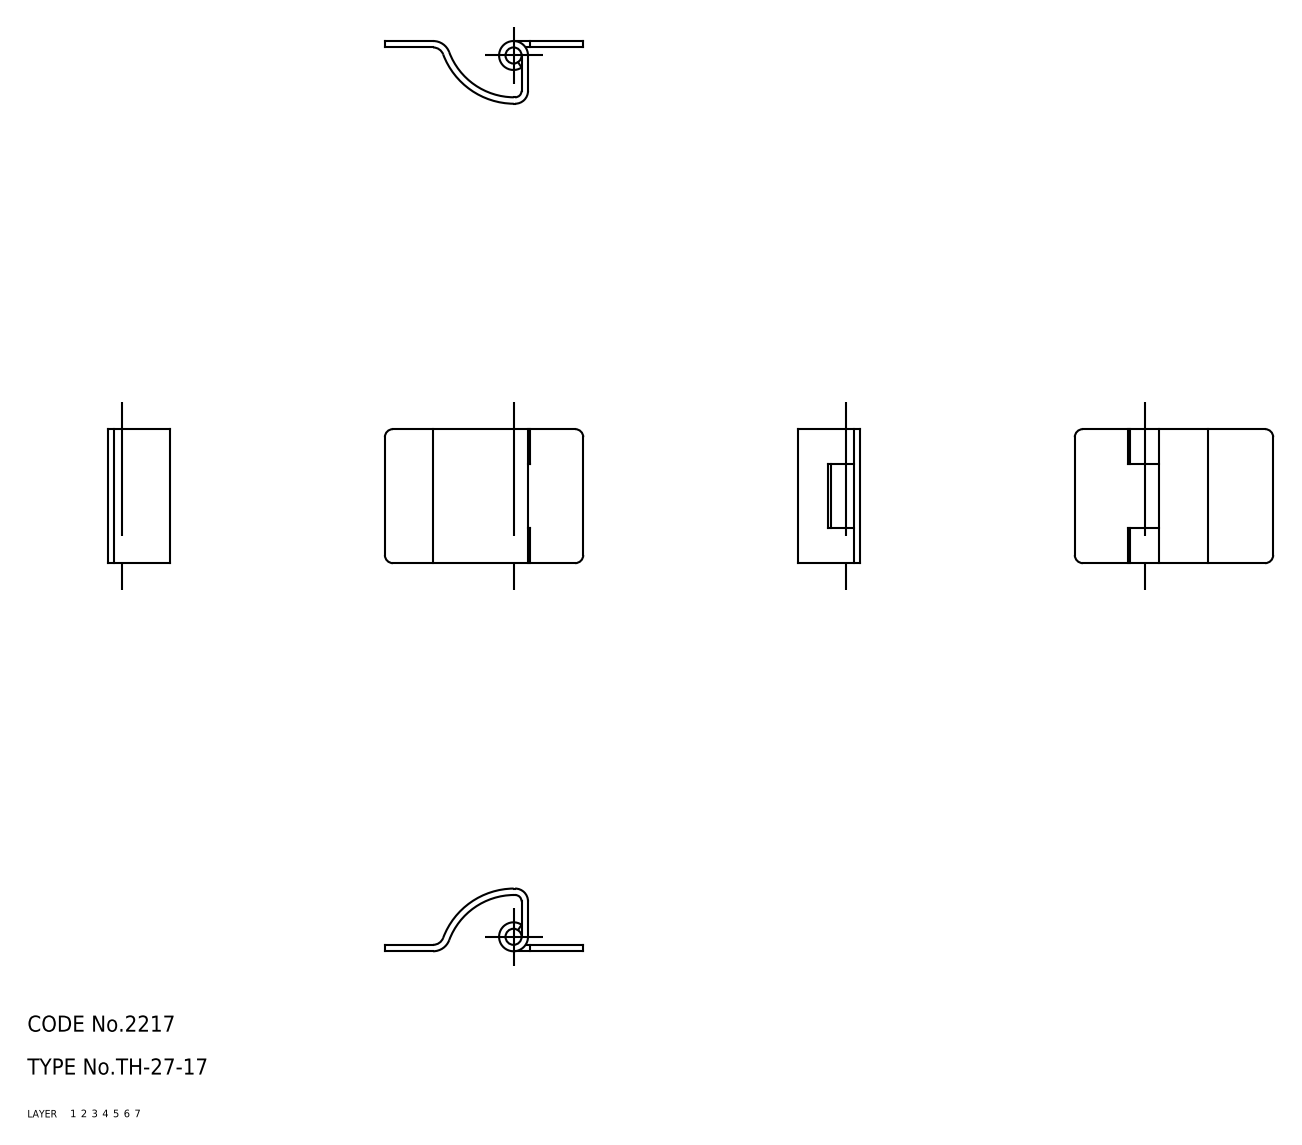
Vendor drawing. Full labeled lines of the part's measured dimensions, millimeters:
Part name (STEP PRODUCT): shaft; hinge piece_B; hinge piece_A; TH_27_17_6926_36
STEP written by: CADfix (AUTOMOTIVE_DESIGN)
Units: millimetres
Bodies: 3 solids, 42 faces (0 planar, 0 cylindrical, 42 other)
Overall size (bounding box): 37 × 25 × 11.7
Volume: 1 949 mm³ · Surface area: 3 530 mm²
